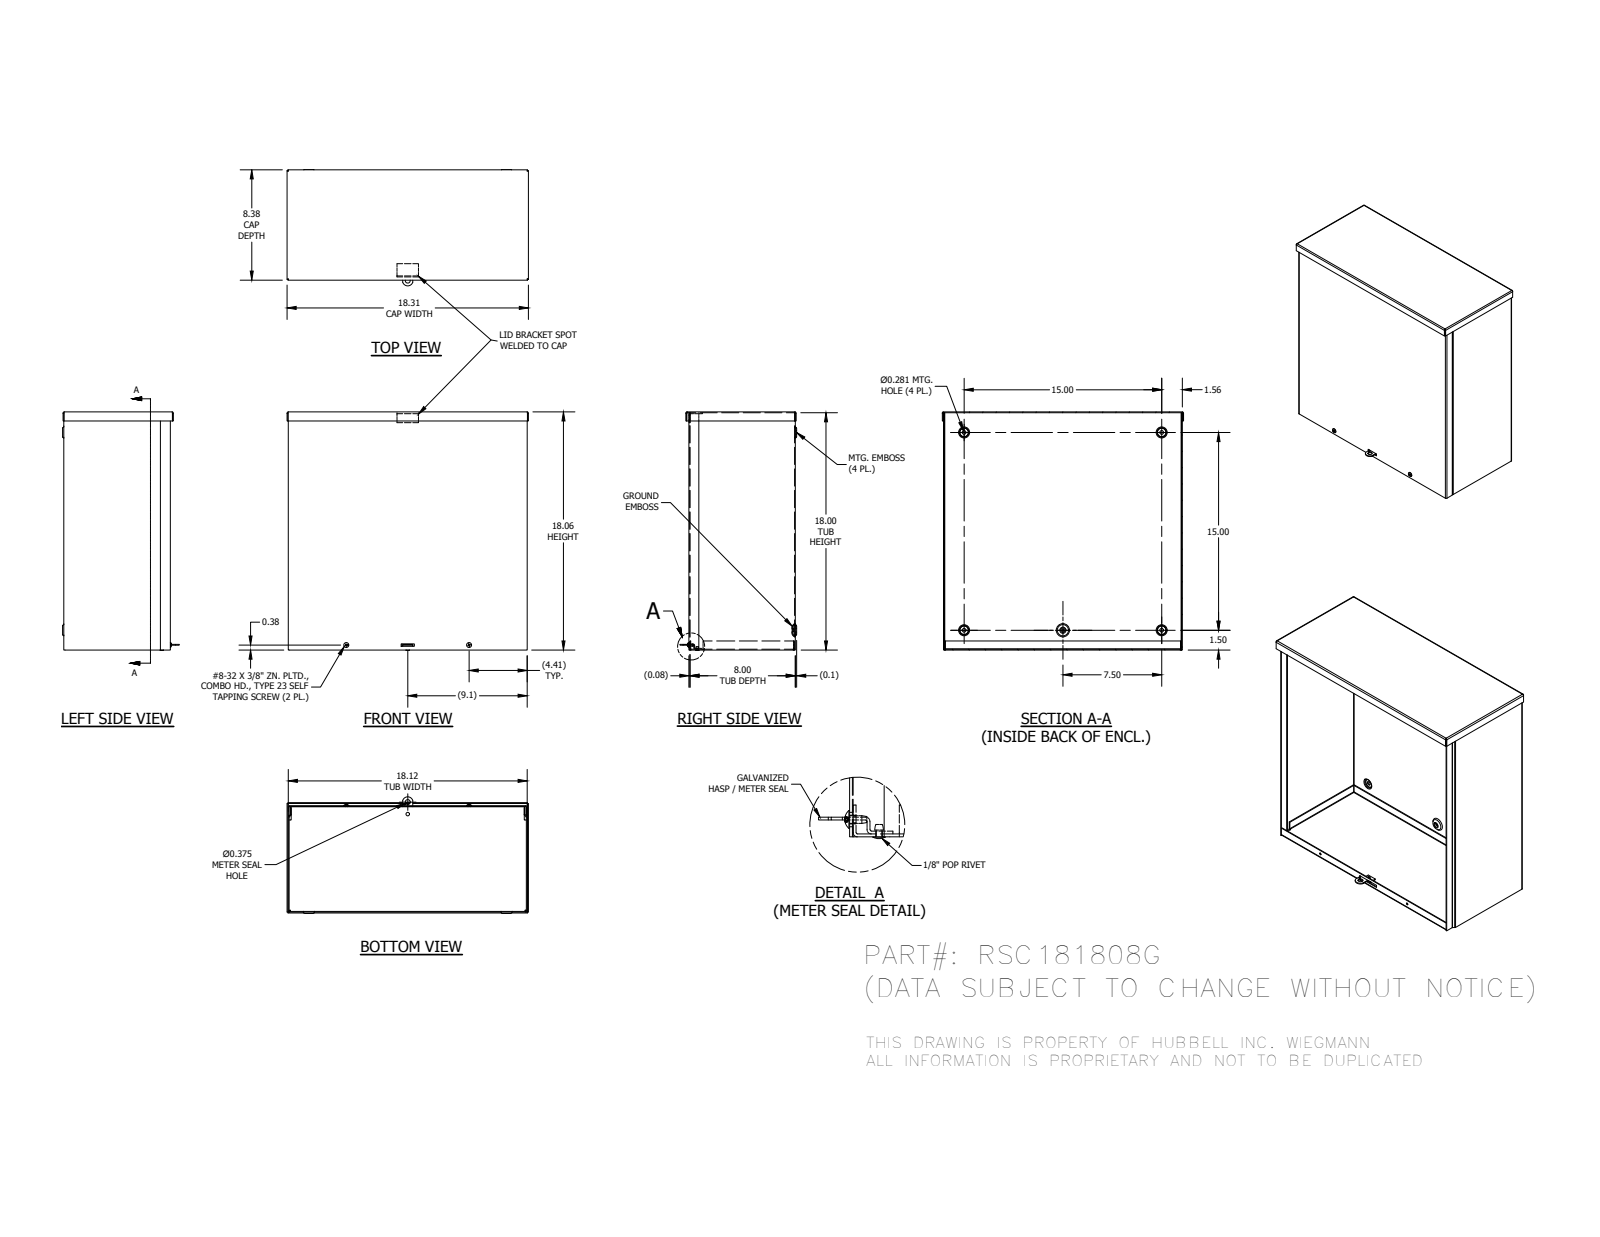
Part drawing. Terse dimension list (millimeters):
name: RSC181808GBKPA; RSC1808GEWPA-16GA; RSC1818GLFA; RSC1808GCPA-16GA (+5 more)
written by: Autodesk Inventor 2014 (AUTOMOTIVE_DESIGN)
unit: mm
bodies: 9 solids, 320 faces (183 planar, 61 cylindrical, 76 other)
size: 465.11 × 459.79 × 224.8
volume: 1 346 000 mm³; area: 1 722 000 mm²
holes: 4× ⌀7.14, 4× ⌀7.94, 2× ⌀3.73, 1× ⌀3.17, 1× ⌀3.45, 1× ⌀4.34, 1× ⌀9.52
bosses: 2× ⌀9.75, 2× ⌀4.17, 1× ⌀6.65, 1× ⌀5.93, 1× ⌀3.17
rounds: 19× R0.79, 18× R2.37, 1× R2.67, 1× R10.16
face distances: 1.57, 203.6, 457.2, 458.77, 205.17, 202.03, 455.63, 460.34, 1.58, 203.2
hole spacings: 77.68, 310.09, 236.54, 121.67, 381, 415.9, 512.93, 190.5
